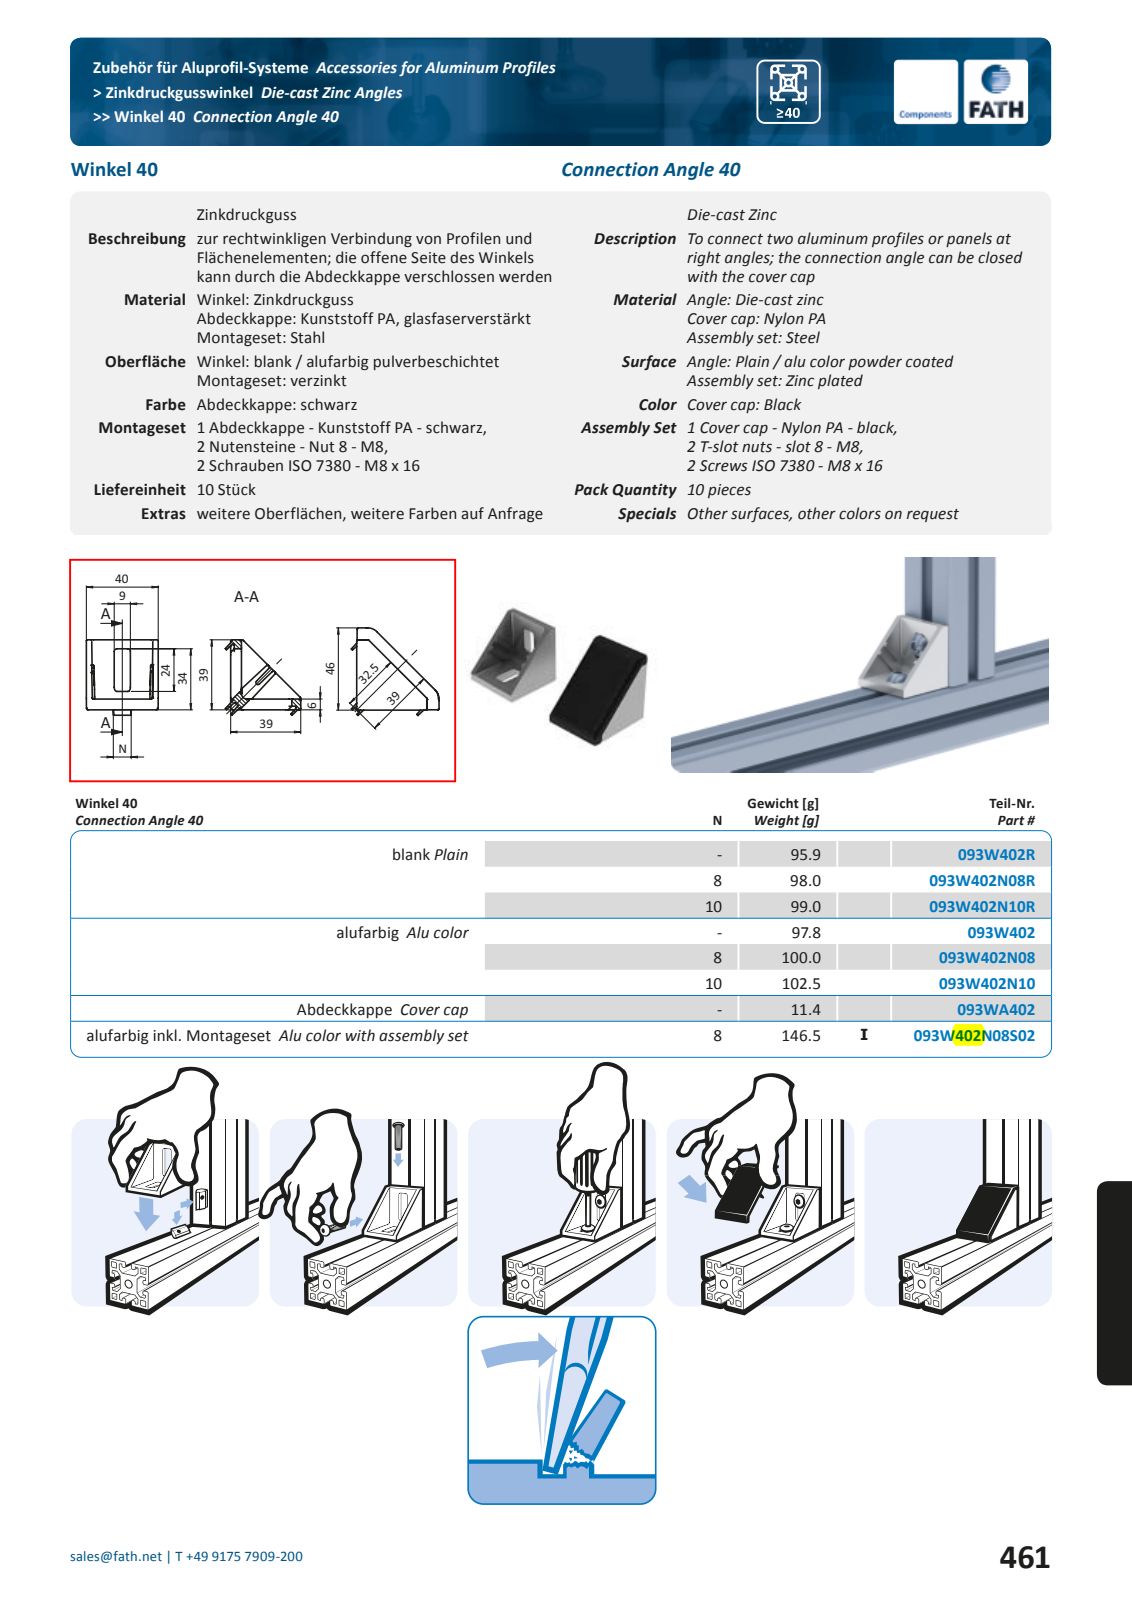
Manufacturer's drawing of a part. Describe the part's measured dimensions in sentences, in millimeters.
The part is named "fath_093wa402". Its 3-D file was written by "Spatial InterOp 3D (automotive_design)". It is 1 solid with 40 faces: 36 planar, 4 cylindrical and 0 other. Overall it measures 64 by 39.6 by 13 millimeters. Its volume is 9 171 cubic millimeters and its surface area 6 911 square millimeters. Partial cylindrical surfaces (rounded edges, fillets, slot ends): 4 of radius 3. The main face-to-face distances are 3, 45.6, 4, 39.6, 1, 55.02, 36.6, 38.9, 6.7, 5.
